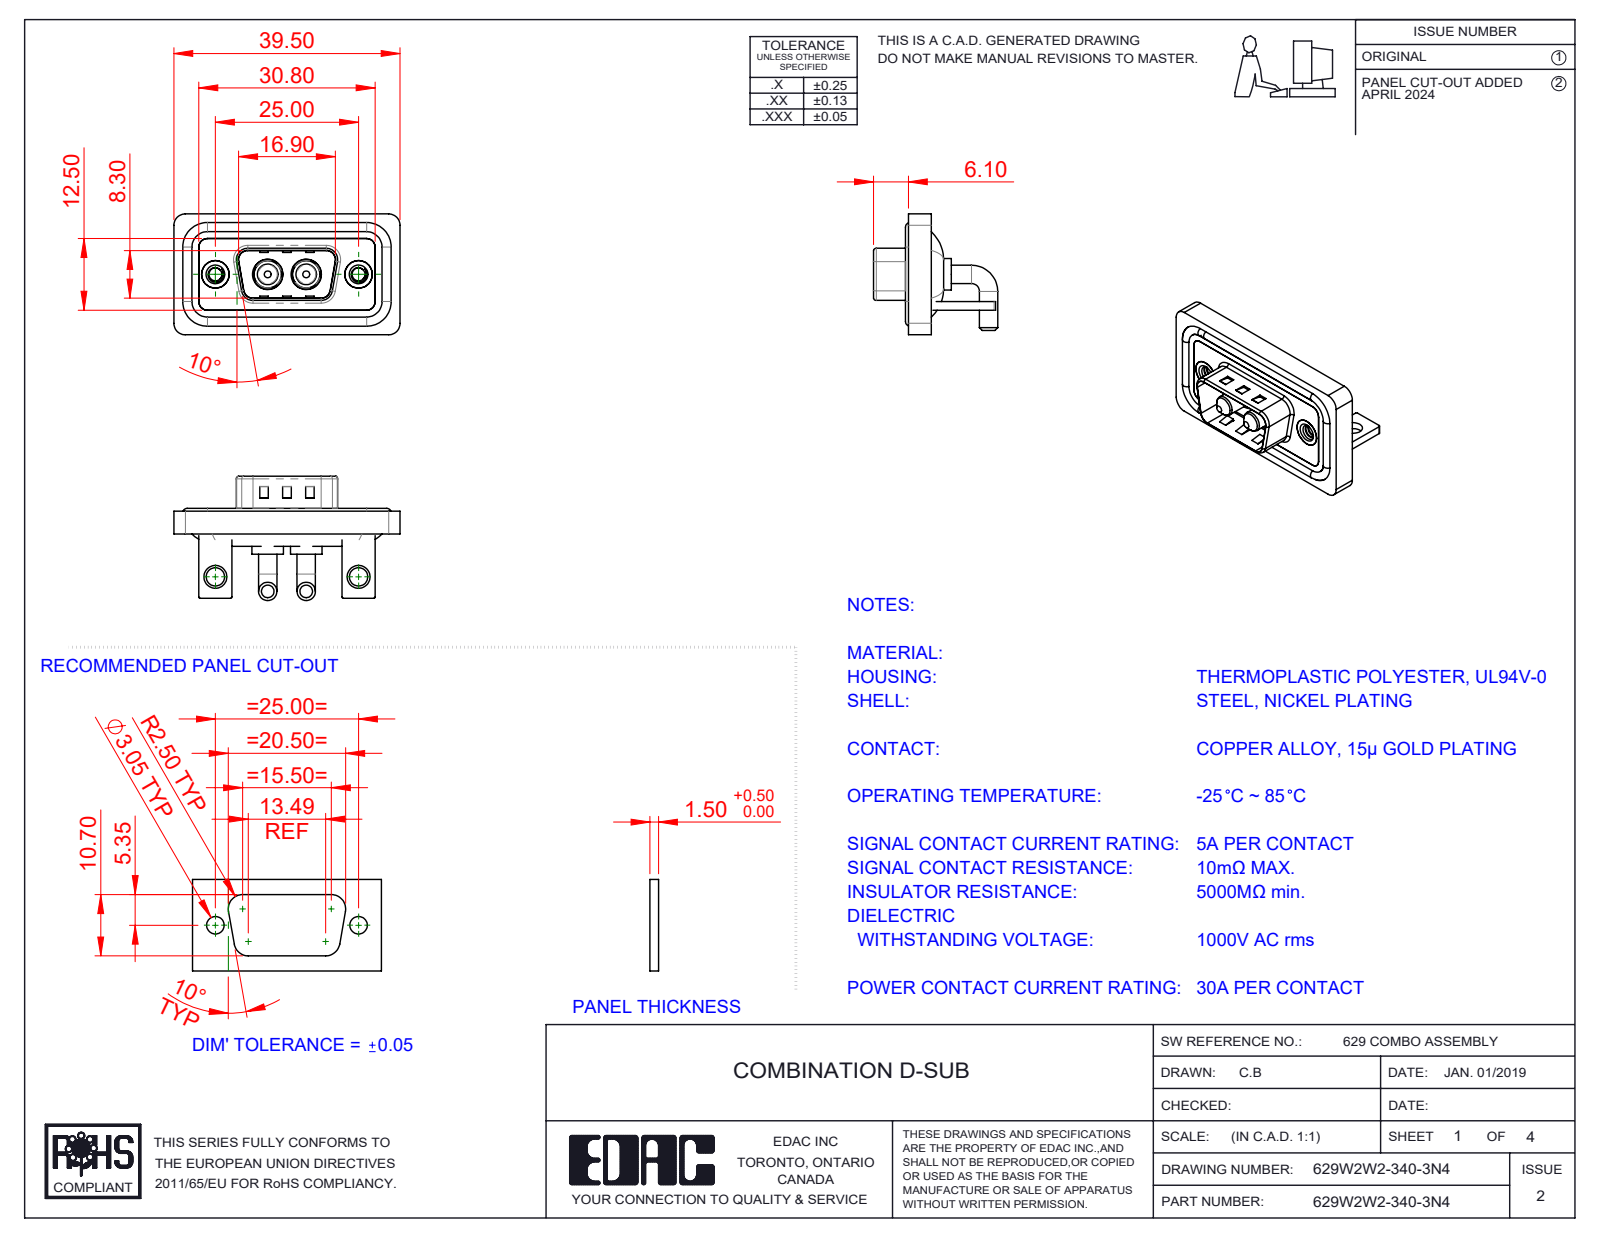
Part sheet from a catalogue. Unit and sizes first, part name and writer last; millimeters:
Units: millimetres
Overall size (bounding box): 39.5 × 21.7 × 21.1
Round holes (diameter × count): ⌀2.26 ×2, ⌀3.2 ×2, ⌀4 ×2, ⌀4.8 ×2, ⌀4.85 ×2, ⌀5 ×2, ⌀5.3 ×2
Round bosses / shafts (diameter × count): ⌀3.2 ×4, ⌀1.6 ×4, ⌀5.5 ×2, ⌀5.2 ×2, ⌀4.9 ×2, ⌀4.75 ×2, ⌀3.75 ×2, ⌀3.6 ×2
Partial cylindrical surfaces — rounded edges, fillets, slot ends (radius × count): R2 ×19, R1.5 ×18, R0.25 ×16, R0.5 ×9, R1.6 ×8, R0.6 ×4, R0.65 ×4, R0.9 ×4
Main face-to-face distances: 0.4, 1.5, 2.9, 0.8, 1.1, 1.2, 2.1, 1.6, 3.7, 2.5
Hole centre spacings: 9.14, 15.86, 25, 6.72
Volume: 4 918 mm³ · Surface area: 7 791 mm²
Bodies: 13 solids, 537 faces (185 planar, 240 cylindrical, 112 other)
Part name (STEP PRODUCT): Power Pin_30A RA; 629Combo Waterproof Housing_09 Contacts; 629Combo Housing_2W2; 629W2W2-340-3N4 (+4 more)
STEP written by: SolidWorks 2023 (CONFIG_CONTROL_DESIGN)
